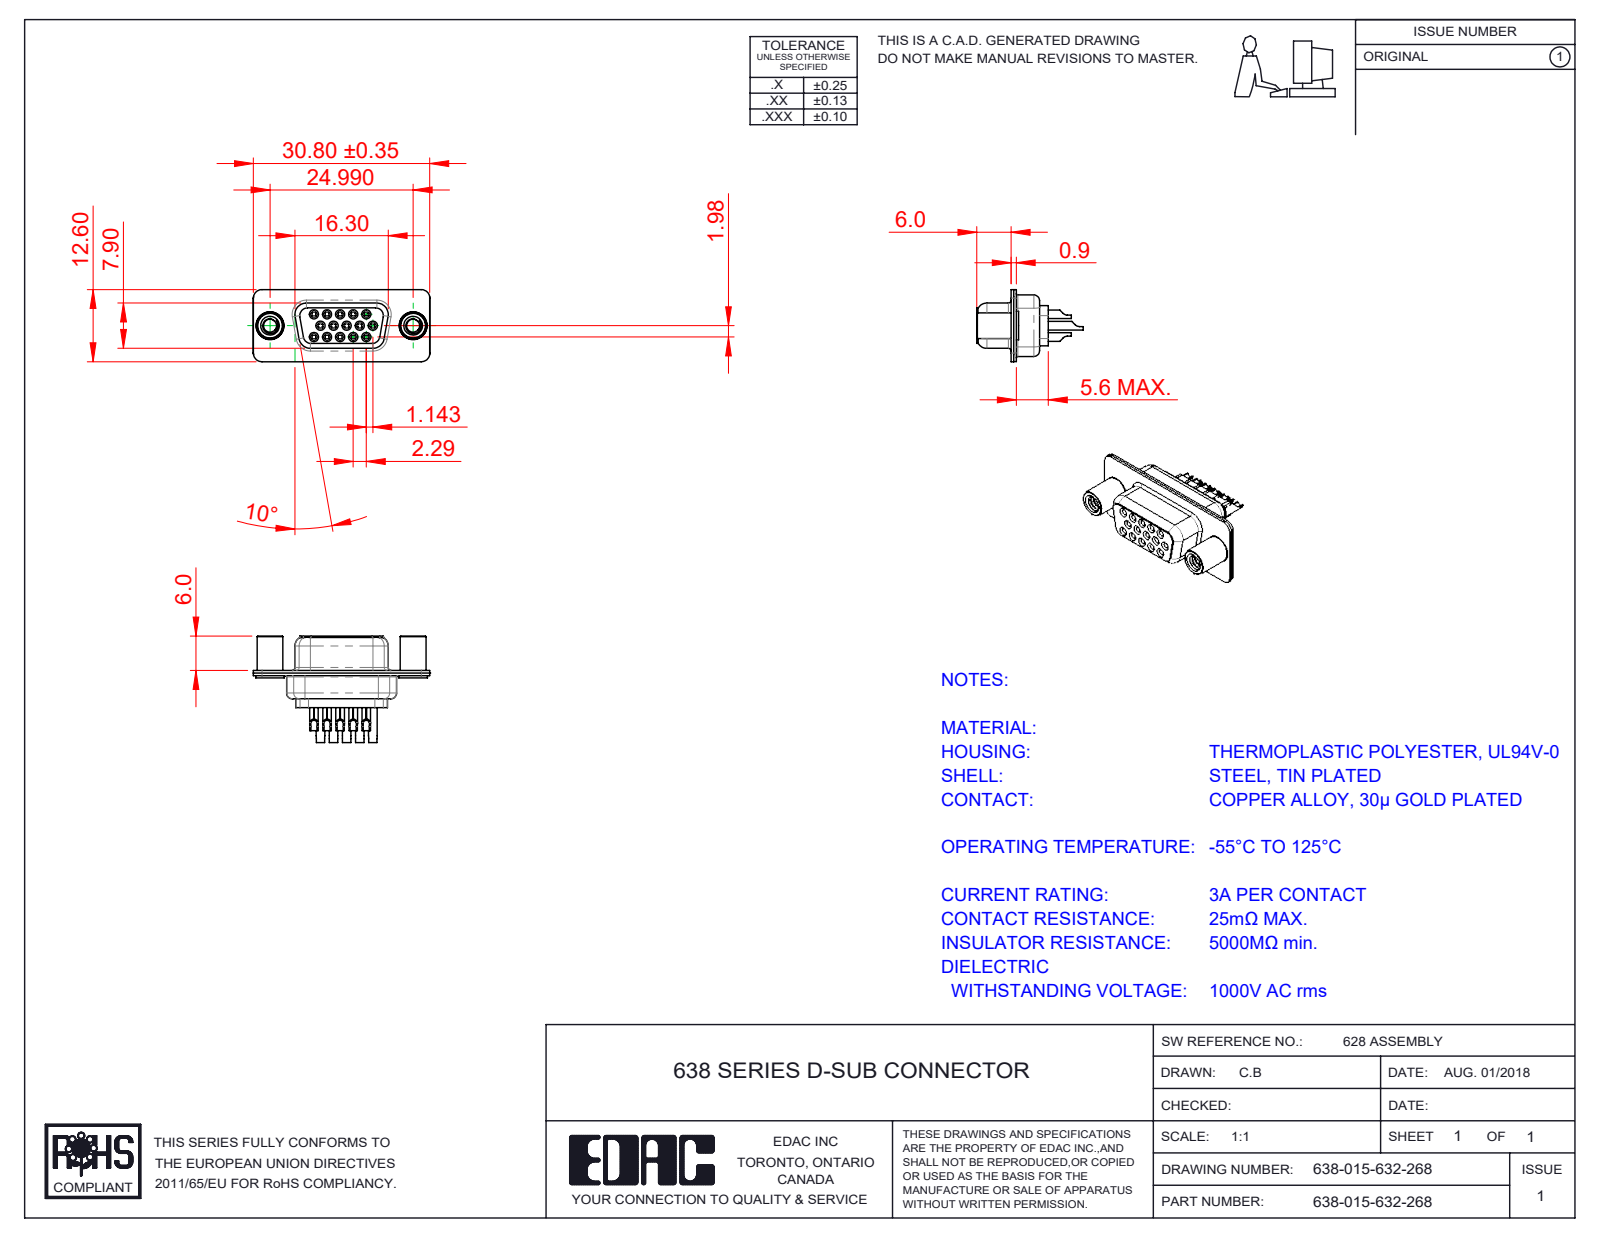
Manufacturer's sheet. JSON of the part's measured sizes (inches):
{"part_name": "638-015-632-268; 638 Shell Rear_15 Contacts; 638 Contact Row 3_32; 638 Contact Row 2_32 (+4 more)", "step_written_by": "SolidWorks 2020 (CONFIG_CONTROL_DESIGN)", "units": "inches", "bodies": {"solids": 20, "faces": 1648, "planar": 384, "cylindrical": 540, "other": 724}, "overall_size": [1.213, 0.732, 0.496], "volume_in3": 0.102, "surface_area_in2": 9.384, "round_holes": [[0.031, 15], [0.039, 15], [0.043, 15], [0.063, 15], [0.067, 15], [0.071, 15], [0.079, 2], [0.089, 2], [0.157, 2], [0.159, 2], [0.191, 2]], "round_bosses_or_shafts": [[0.079, 15], [0.059, 15], [0.047, 15], [0.197, 2], [0.195, 2], [0.189, 2], [0.177, 2]], "partial_cylinders_radius": [[0.059, 20], [0.079, 12], [0.011, 10], [0.061, 8], [0.039, 7], [0.053, 5], [0.01, 4], [0.02, 4]], "face_to_face_distances": [0.018, 0.035, 0.016, 0.056, 0.35, 0.26, 0.055, 0.033, 0.09, 0.071], "hole_center_spacings": [0.156, 0.09, 0.18, 0.09, 0.238, 0.238, 0.27, 0.312]}
